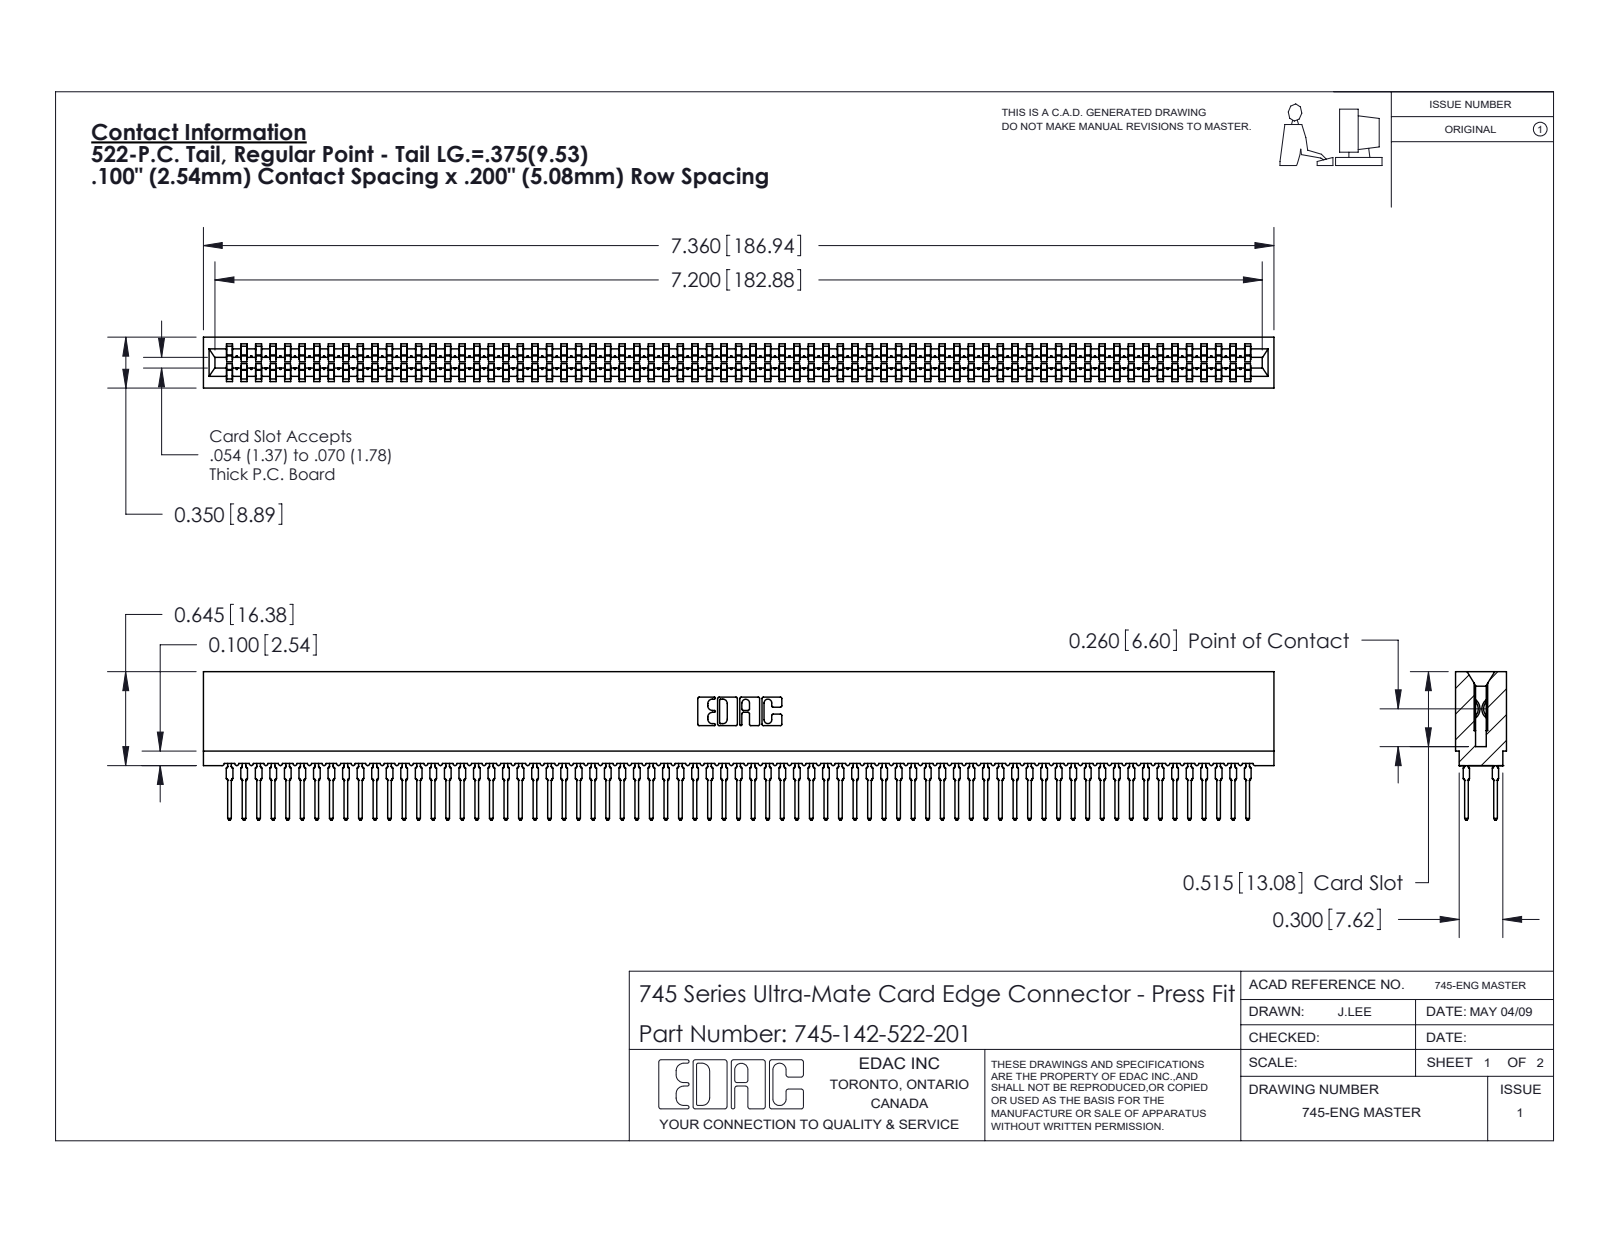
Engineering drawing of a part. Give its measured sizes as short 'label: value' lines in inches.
name: 745-142-522-201; 745 Part_Insulator Option - 01; 745-292-001_522
written by: SolidWorks 2020 (CONFIG_CONTROL_DESIGN)
unit: in
bodies: 143 solids, 12804 faces (6587 planar, 2525 cylindrical, 3692 other)
size: 7.36 × 1.021 × 0.35
volume: 1.026 in³; area: 54.77 in²
rounds: 284× R0.021, 142× R0.015, 22× R0.01, 8× R0.005, 8× R0.011, 6× R0.007, 6× R0.031, 3× R0.026
face distances: 0.35, 0.063, 0.287, 0.045, 0.305, 0.018, 0.243, 0.138, 0.212, 0.093
